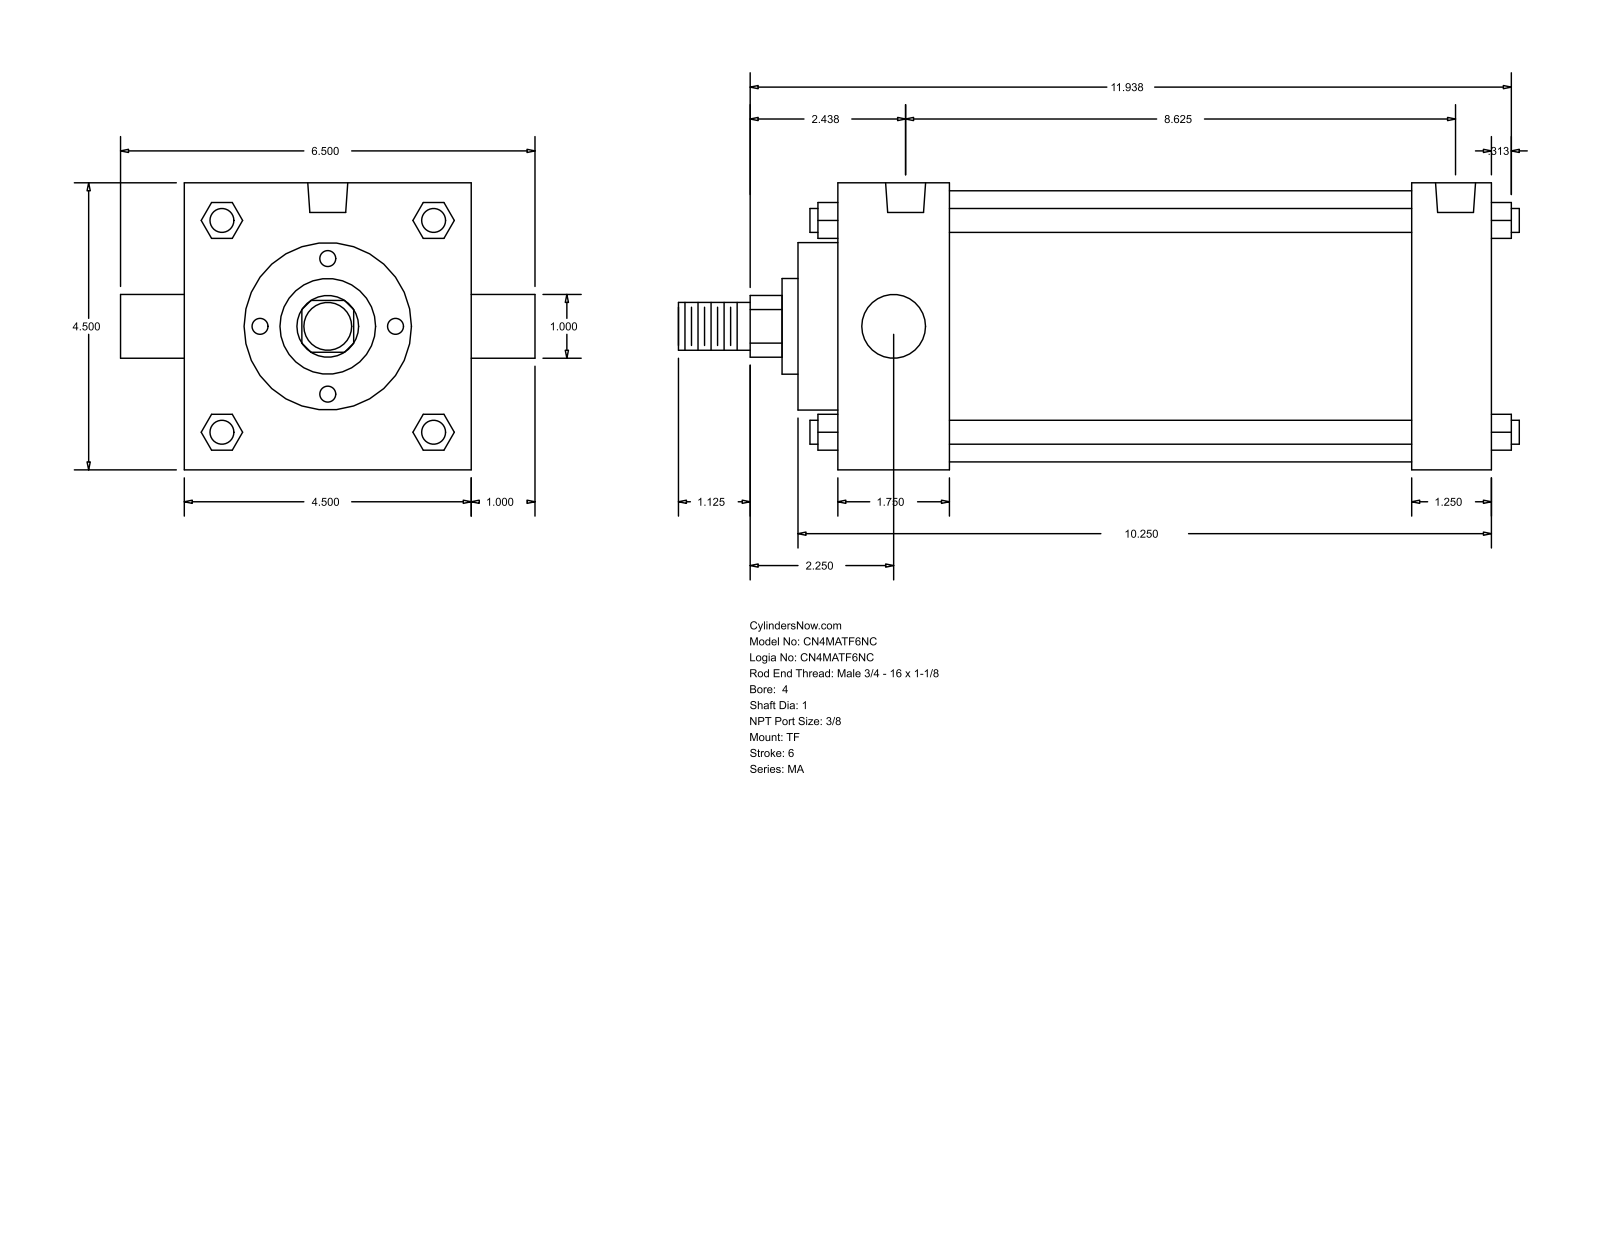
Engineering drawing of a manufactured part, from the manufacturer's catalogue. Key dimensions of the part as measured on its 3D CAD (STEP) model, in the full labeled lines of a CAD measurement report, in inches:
Part name (STEP PRODUCT): MA_TF__0400_1
STEP written by: GSSL Pune (CONFIG_CONTROL_DESIGN)
Units: inches
Bodies: 0 solids, 122 faces (93 planar, 29 cylindrical, 0 other)
Overall size (bounding box): 13.187 × 6.5 × 4.5
Round holes (diameter × count): ⌀0.437 ×3, ⌀0.627 ×2
Round bosses / shafts (diameter × count): ⌀0.375 ×4, ⌀1 ×2, ⌀4.25 ×1, ⌀2.625 ×1, ⌀1.5 ×1, ⌀0.75 ×1
Partial cylindrical surfaces — rounded edges, fillets, slot ends (radius × count): R0.484 ×1
Main face-to-face distances: 4.5, 10.25, 9, 1.25, 1.75, 7.25, 8.5, 10.875, 0.625, 2.375
Hole centre spacings: 0.187, 8.438, 8.25, 8.625
